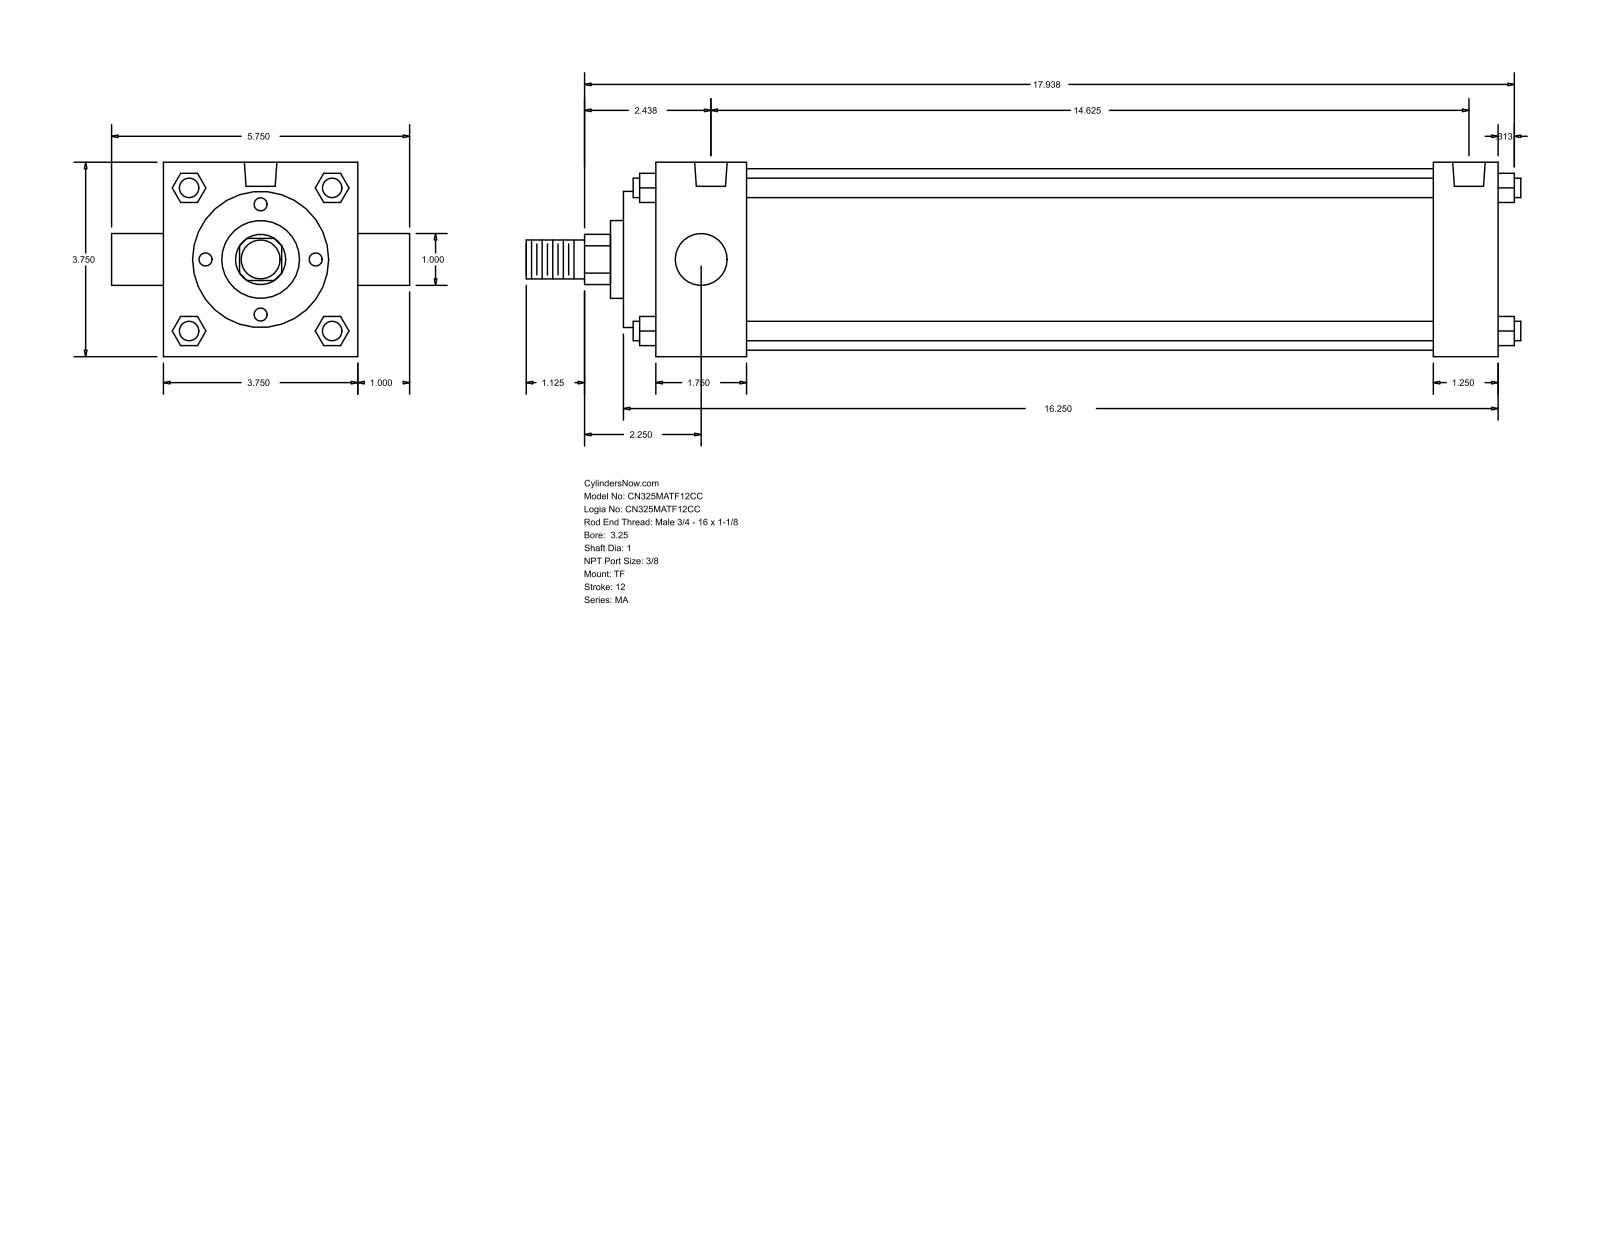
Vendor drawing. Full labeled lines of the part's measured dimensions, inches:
Part name (STEP PRODUCT): MA_TF__0325_1
STEP written by: GSSL Pune (CONFIG_CONTROL_DESIGN)
Units: inches
Bodies: 0 solids, 122 faces (93 planar, 29 cylindrical, 0 other)
Overall size (bounding box): 19.187 × 5.75 × 3.75
Round holes (diameter × count): ⌀0.437 ×3, ⌀0.627 ×2
Round bosses / shafts (diameter × count): ⌀0.375 ×4, ⌀1 ×2, ⌀3.5 ×1, ⌀2.625 ×1, ⌀1.5 ×1, ⌀0.75 ×1
Partial cylindrical surfaces — rounded edges, fillets, slot ends (radius × count): R0.484 ×1
Main face-to-face distances: 3.75, 16.25, 1.75, 15, 13.25, 14.5, 1.25, 0.625, 2.375, 15.625
Hole centre spacings: 0.187, 0.188, 14.25, 14.437, 14.438, 14.625
